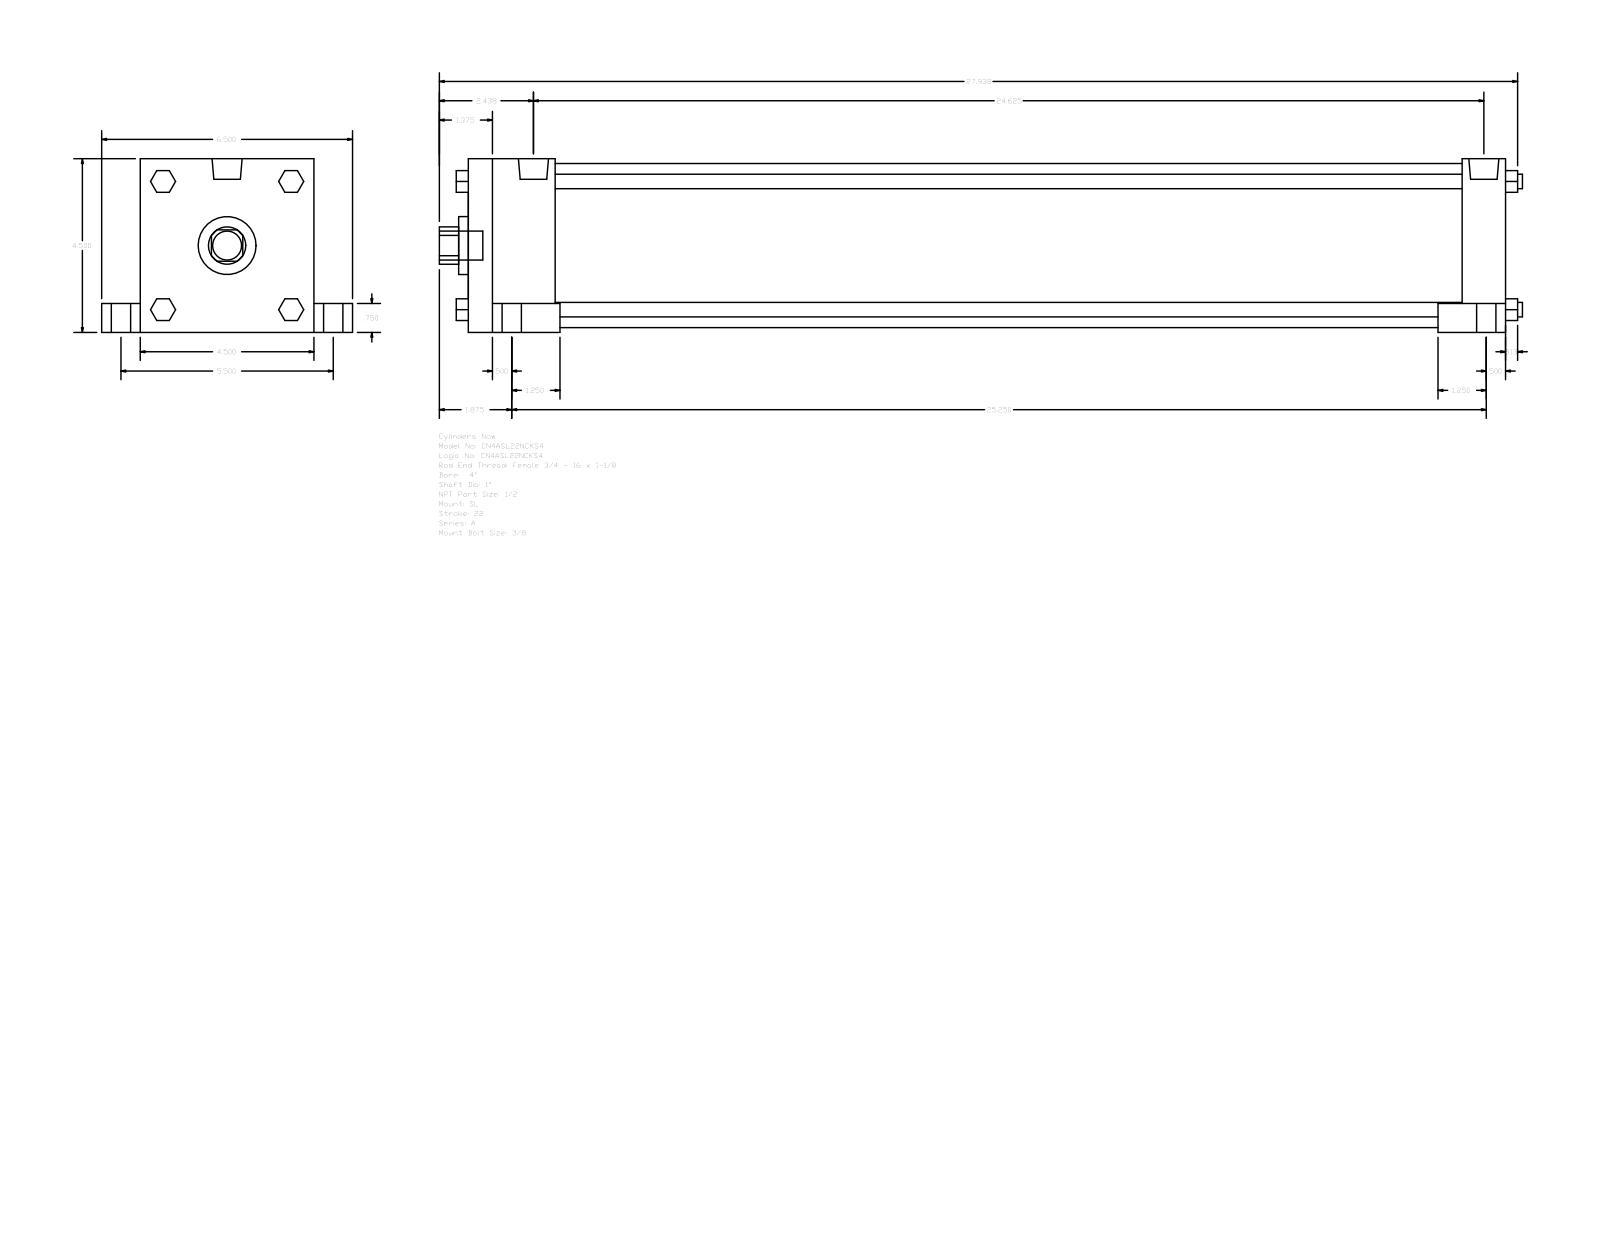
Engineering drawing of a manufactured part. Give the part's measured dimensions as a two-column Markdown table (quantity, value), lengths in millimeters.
| quantity | value |
| --- | --- |
| part name | A_SL__0400_1 |
| STEP written by | GSSL Pune (CONFIG_CONTROL_DESIGN) |
| units | millimeters |
| bodies | 0 solids, 150 faces (114 planar, 36 cylindrical, 0 other) |
| overall size | 712.79 × 165.1 × 114.3 |
| round holes (diameter × count) | 25.4 × 1, 38.1 × 1, 107.95 × 1 |
| round bosses / shafts (diameter × count) | 19.05 × 5, 12.7 × 4, 9.53 × 4, 8.73 × 4, 19.77 × 2 |
| partial cylindrical surfaces (radius × count) | 12.29 × 1 |
| main face-to-face distances | 114.3, 682.62, 28.57, 57.15, 625.47, 654.05, 596.9, 19.05, 25.4, 139.7 |
